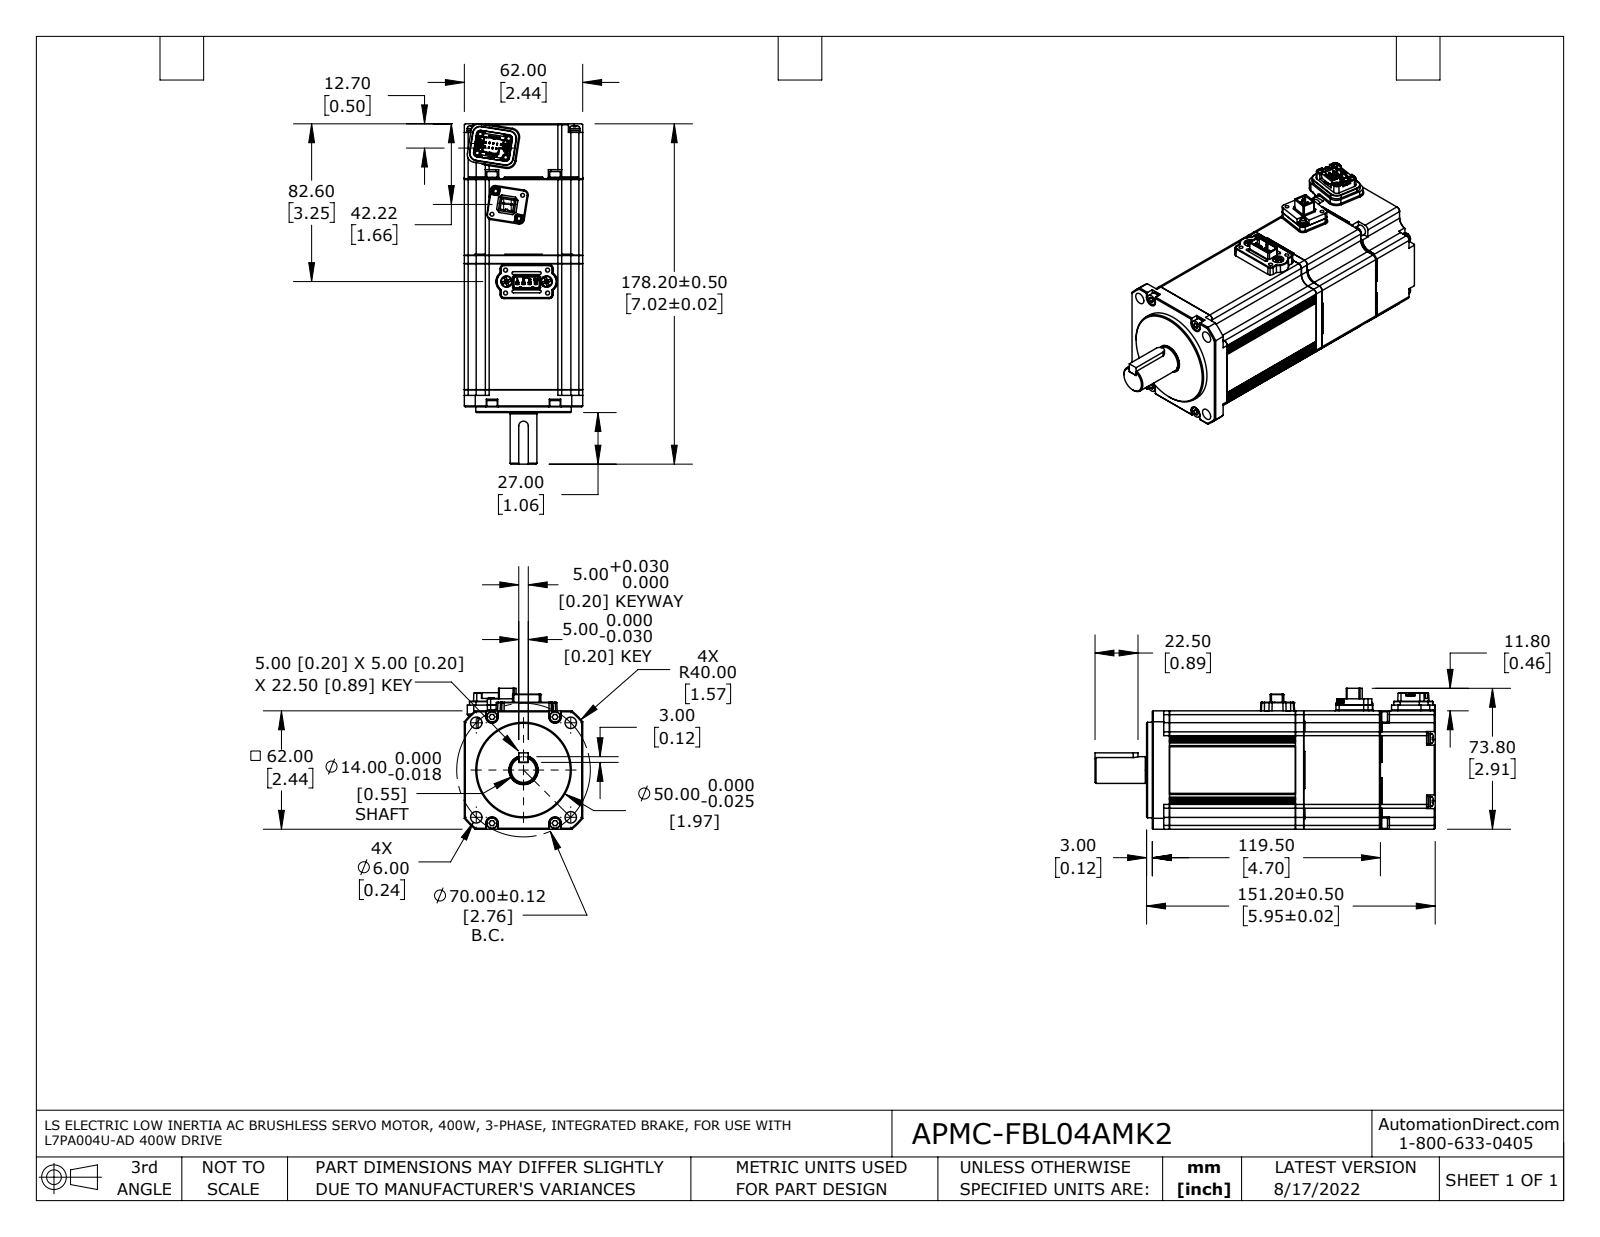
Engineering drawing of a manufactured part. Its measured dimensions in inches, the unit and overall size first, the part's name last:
Units: inches
Overall size (bounding box): 7.016 × 2.906 × 2.441
Round holes (diameter × count): ⌀0.083 ×10, ⌀0.118 ×10, ⌀0.138 ×8, ⌀0.079 ×6, ⌀0.236 ×6, ⌀0.122 ×4, ⌀0.039 ×2, ⌀0.13 ×1, ⌀0.134 ×1, ⌀0.512 ×1, ⌀0.602 ×1
Round bosses / shafts (diameter × count): ⌀0.213 ×6, ⌀0.22 ×4, ⌀0.217 ×4, ⌀0.165 ×2, ⌀0.142 ×2, ⌀0.138 ×2, ⌀0.087 ×2, ⌀0.035 ×2
Partial cylindrical surfaces — rounded edges, fillets, slot ends (radius × count): R0.008 ×20, R0.012 ×20, R0.039 ×14, R0.079 ×12, R0.006 ×9, R0.118 ×8, R0.018 ×7, R0.004 ×6
Main face-to-face distances: 2.441, 0.169, 0.028, 0.02, 2.598, 2.768, 1.752, 1.583, 4.35, 1.61
Hole centre spacings: 0.237, 0.335, 0.346, 0.371, 0.602, 0.63, 0.879, 1.239
Volume: 31.5 in³ · Surface area: 160.5 in²
Bodies: 51 solids, 2101 faces (1289 planar, 602 cylindrical, 210 other)
Part name (STEP PRODUCT): SLM06GA003G03_Out Line(APMC-FBL04AMK2) r1 nc fxt
STEP written by: SolidWorks 2017 (AUTOMOTIVE_DESIGN)
